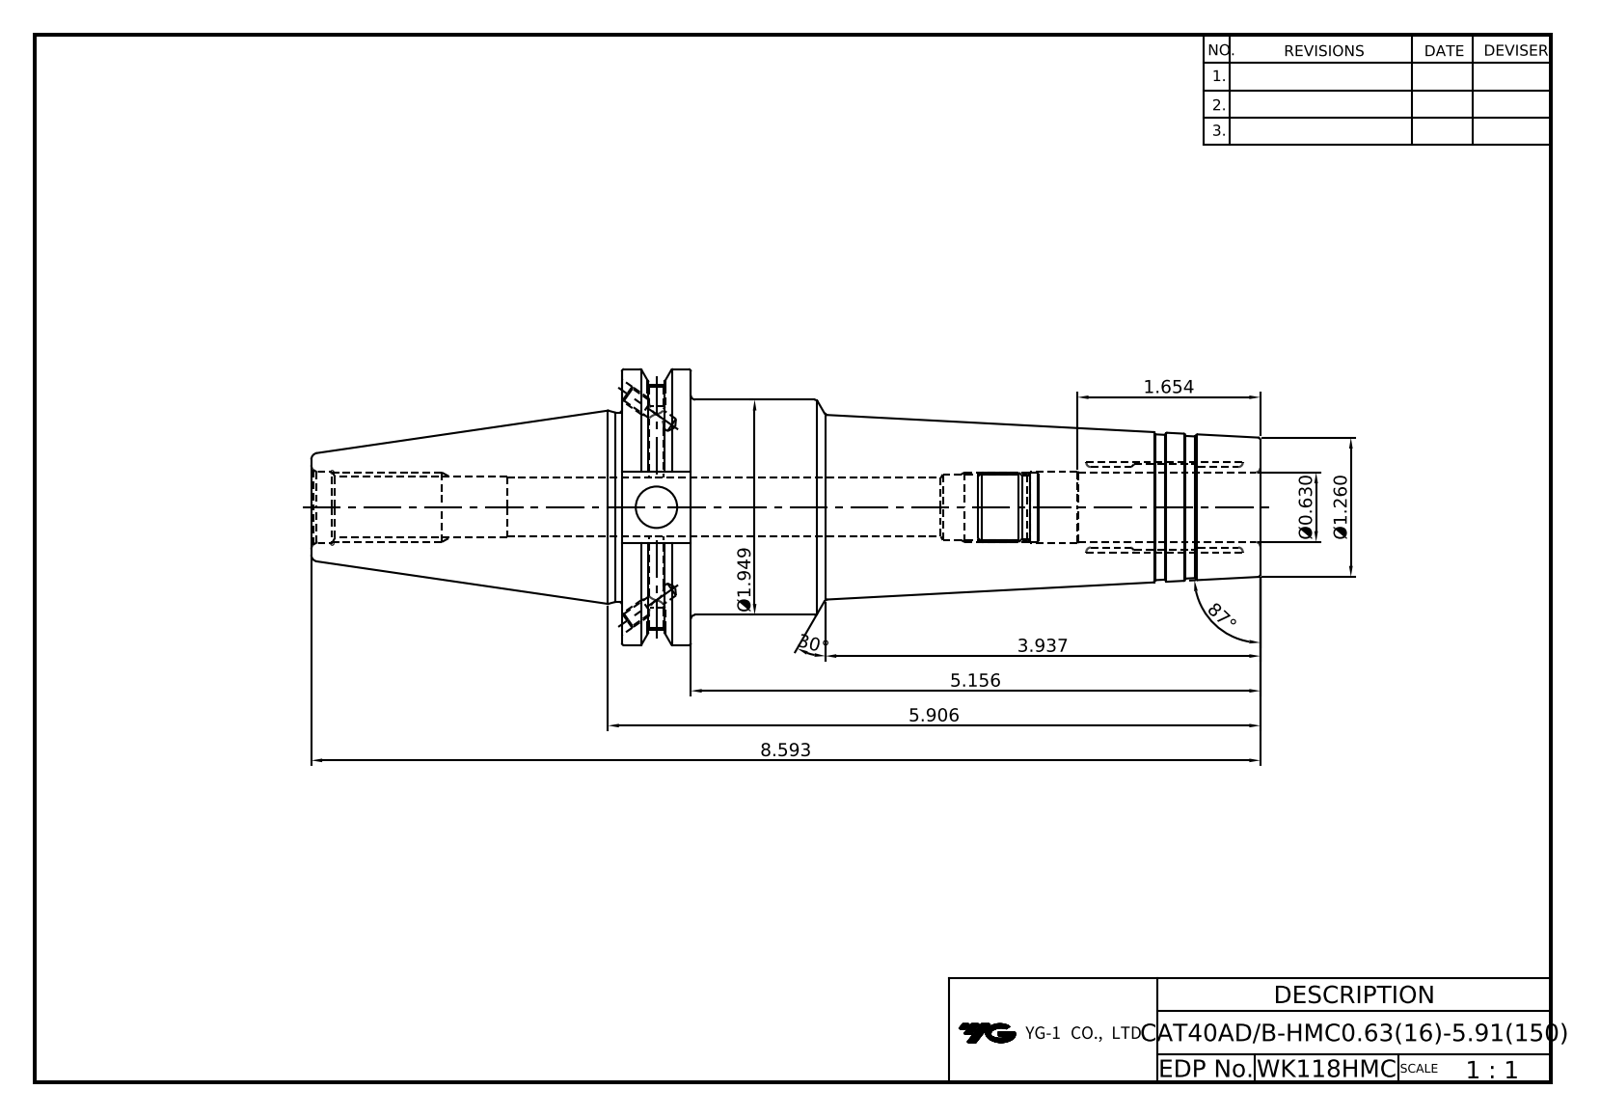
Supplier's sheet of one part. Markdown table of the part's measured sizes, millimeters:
| quantity | value |
| --- | --- |
| part name | LO-CAT40ADB-HMC16-150 |
| STEP written by | Autodesk Inventor 2020 (AUTOMOTIVE_DESIGN) |
| units | millimeters |
| bodies | 1 solid, 106 faces (36 planar, 30 cylindrical, 40 other) |
| overall size | 218.25 × 63.5 × 61.09 |
| volume | 248 448 mm³ |
| surface area | 42 179 mm² |
| round holes (diameter × count) | 3.24 × 4, 4 × 2, 4.2 × 2, 9.53 × 1, 10.92 × 1, 13 × 1, 13.39 × 1, 16 × 1, 16.3 × 1, 16.6 × 1 |
| round bosses / shafts (diameter × count) | 63.5 × 1, 49.5 × 1, 43.6 × 1 |
| partial cylindrical surfaces (radius × count) | 8.19 × 1, 28.15 × 1 |
| main face-to-face distances | 15.88, 146.83, 130.95, 47.6, 16.38, 71.42, 87.3, 218.25, 167.25, 95.83 |
